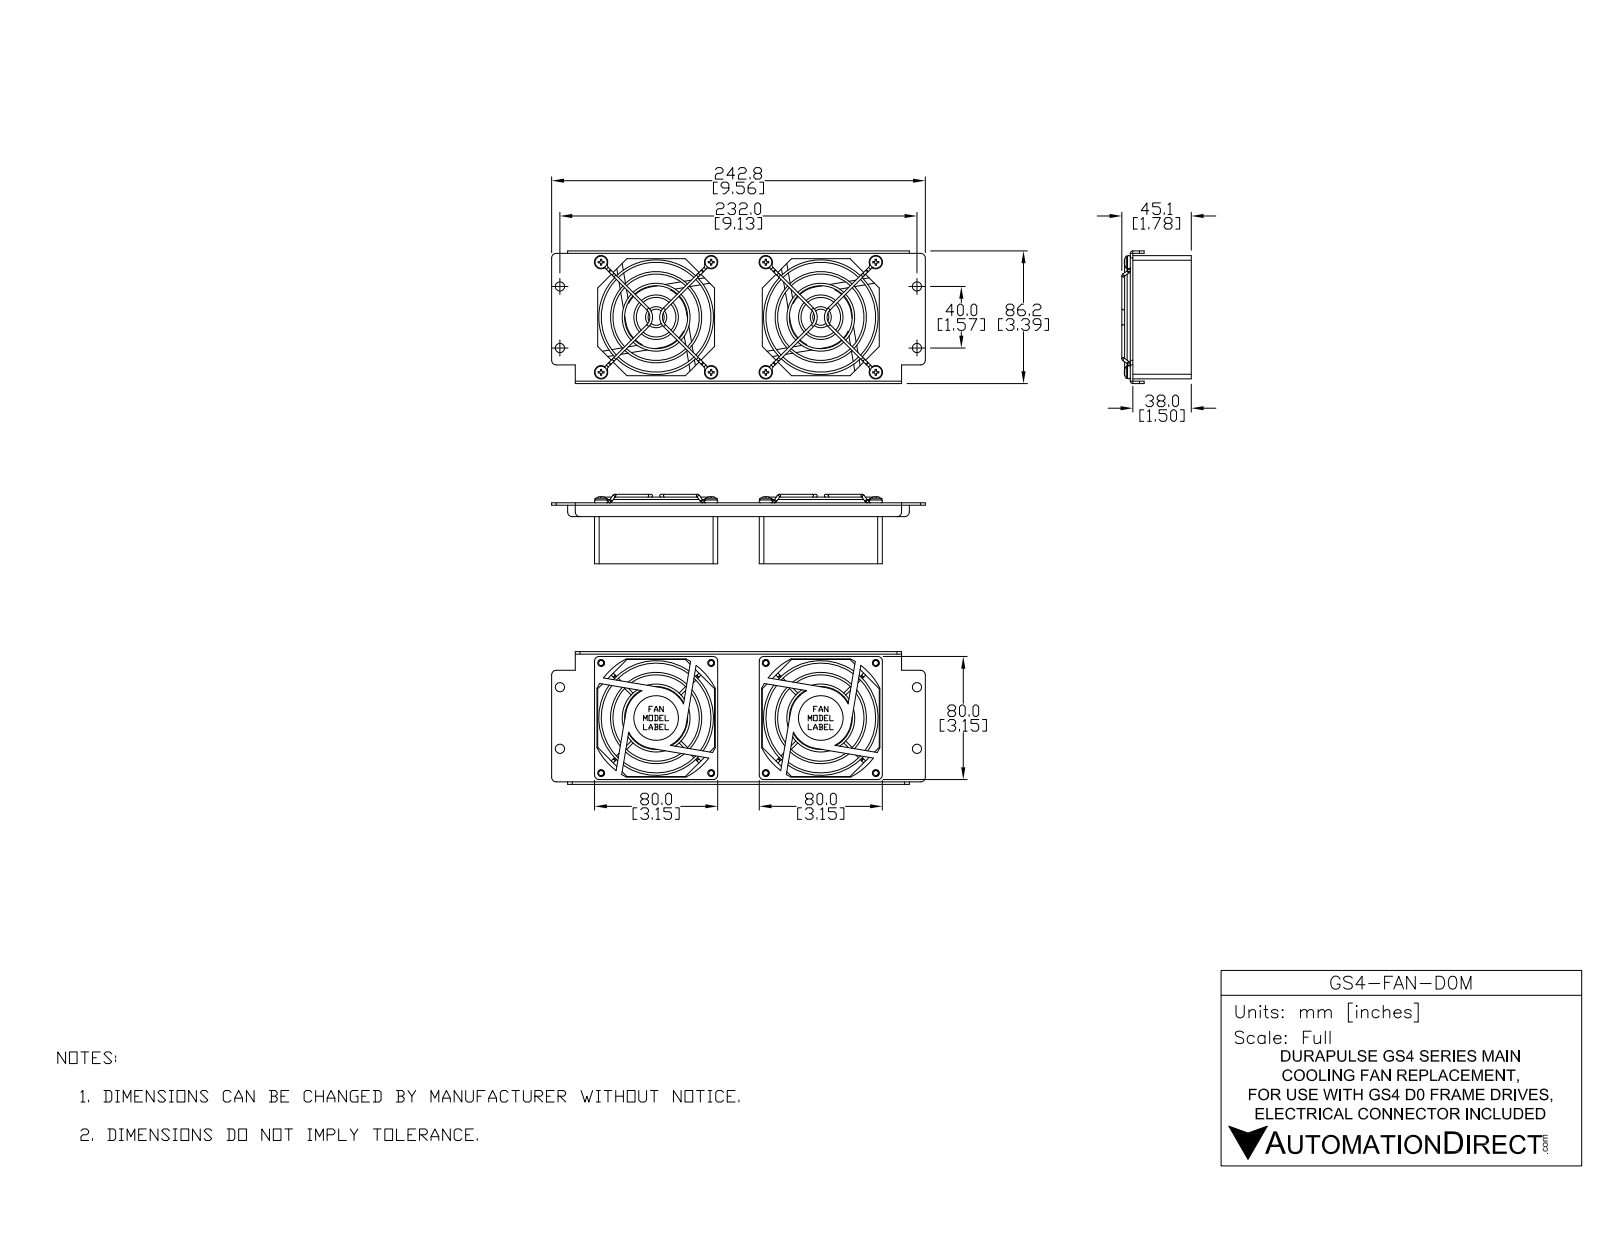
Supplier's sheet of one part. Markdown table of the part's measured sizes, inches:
| quantity | value |
| --- | --- |
| part name | GS4-FAN-D0M |
| STEP written by | SolidWorks 2015 (AUTOMOTIVE_DESIGN) |
| units | inches |
| bodies | 0 solids, 360 faces (86 planar, 130 cylindrical, 144 other) |
| overall size | 9.559 × 3.394 × 1.776 |
| round holes (diameter × count) | 0.177 × 8, 0.236 × 4 |
| round bosses / shafts (diameter × count) | 0.071 × 24, 0.311 × 8 |
| partial cylindrical surfaces (radius × count) | 0.118 × 16, 0.063 × 2, 0.787 × 2, 1.693 × 2 |
| main face-to-face distances | 0.063, 3.087, 3.15, 4.213, 0.158, 1.418, 0.122, 3.209, 3.024, 1.576 |
| hole center spacings | 2.815, 1.222, 2.435, 3.917, 3.981, 4.213, 4.448, 5.067 |
